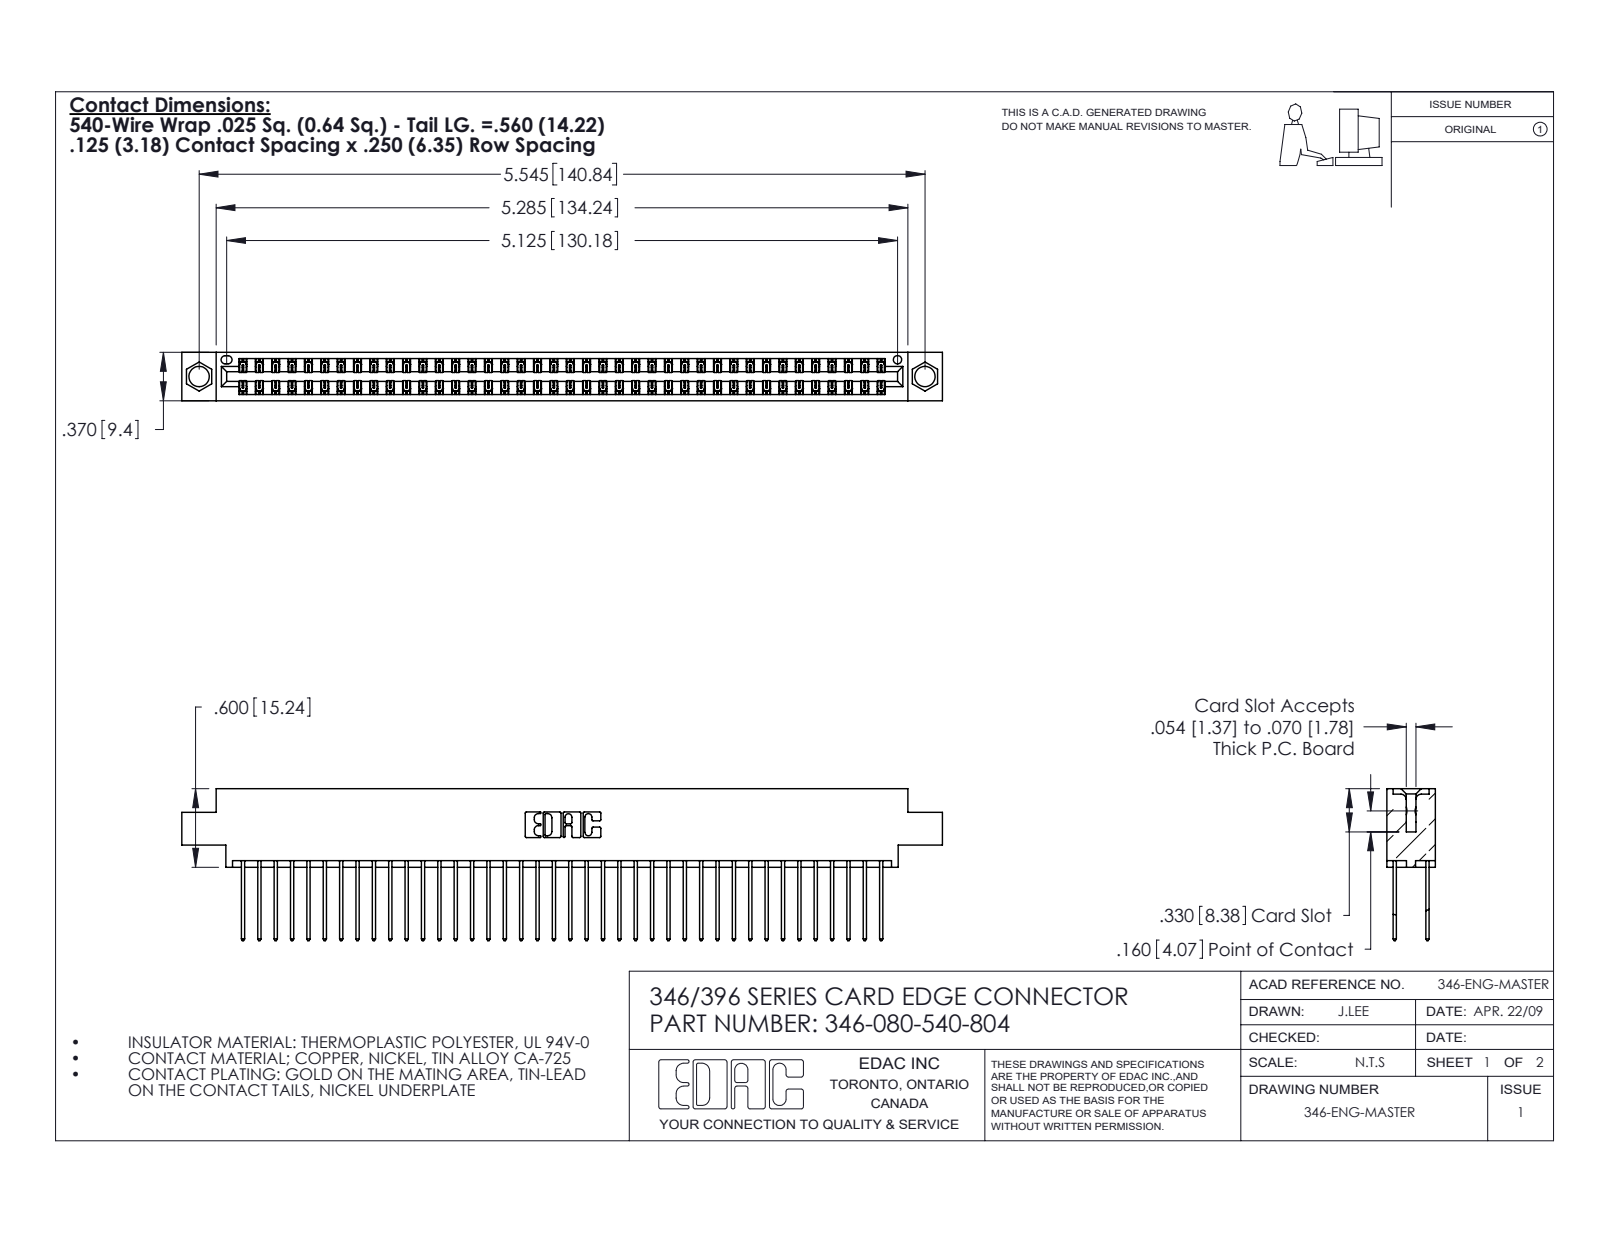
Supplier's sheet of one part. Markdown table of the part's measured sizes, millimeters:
| quantity | value |
| --- | --- |
| part name | 346 Part_0.170 Offset - 0.156 Dia-TH; 345-292-001_345-293-140; 346-080-540-804 |
| STEP written by | SolidWorks 2020 (CONFIG_CONTROL_DESIGN) |
| units | millimeters |
| bodies | 81 solids, 4300 faces (2894 planar, 1406 cylindrical, 0 other) |
| overall size | 147.6 × 29.5 × 9.4 |
| volume | 14 400 mm³ |
| surface area | 21 250 mm² |
| round holes (diameter × count) | 4 × 2, 1.6 × 1 |
| partial cylindrical surfaces (radius × count) | 0.2 × 120, 0.3 × 80, 0.3 × 22, 0.2 × 6, 0.8 × 6, 0.7 × 3, 0.4 × 2, 0.6 × 2 |
| main face-to-face distances | 1.2, 8.2, 6.4, 1.8, 7.6, 0.6, 9.4, 7, 5.6, 3.8 |
| hole center spacings | 6.2, 135.5, 140.8 |
